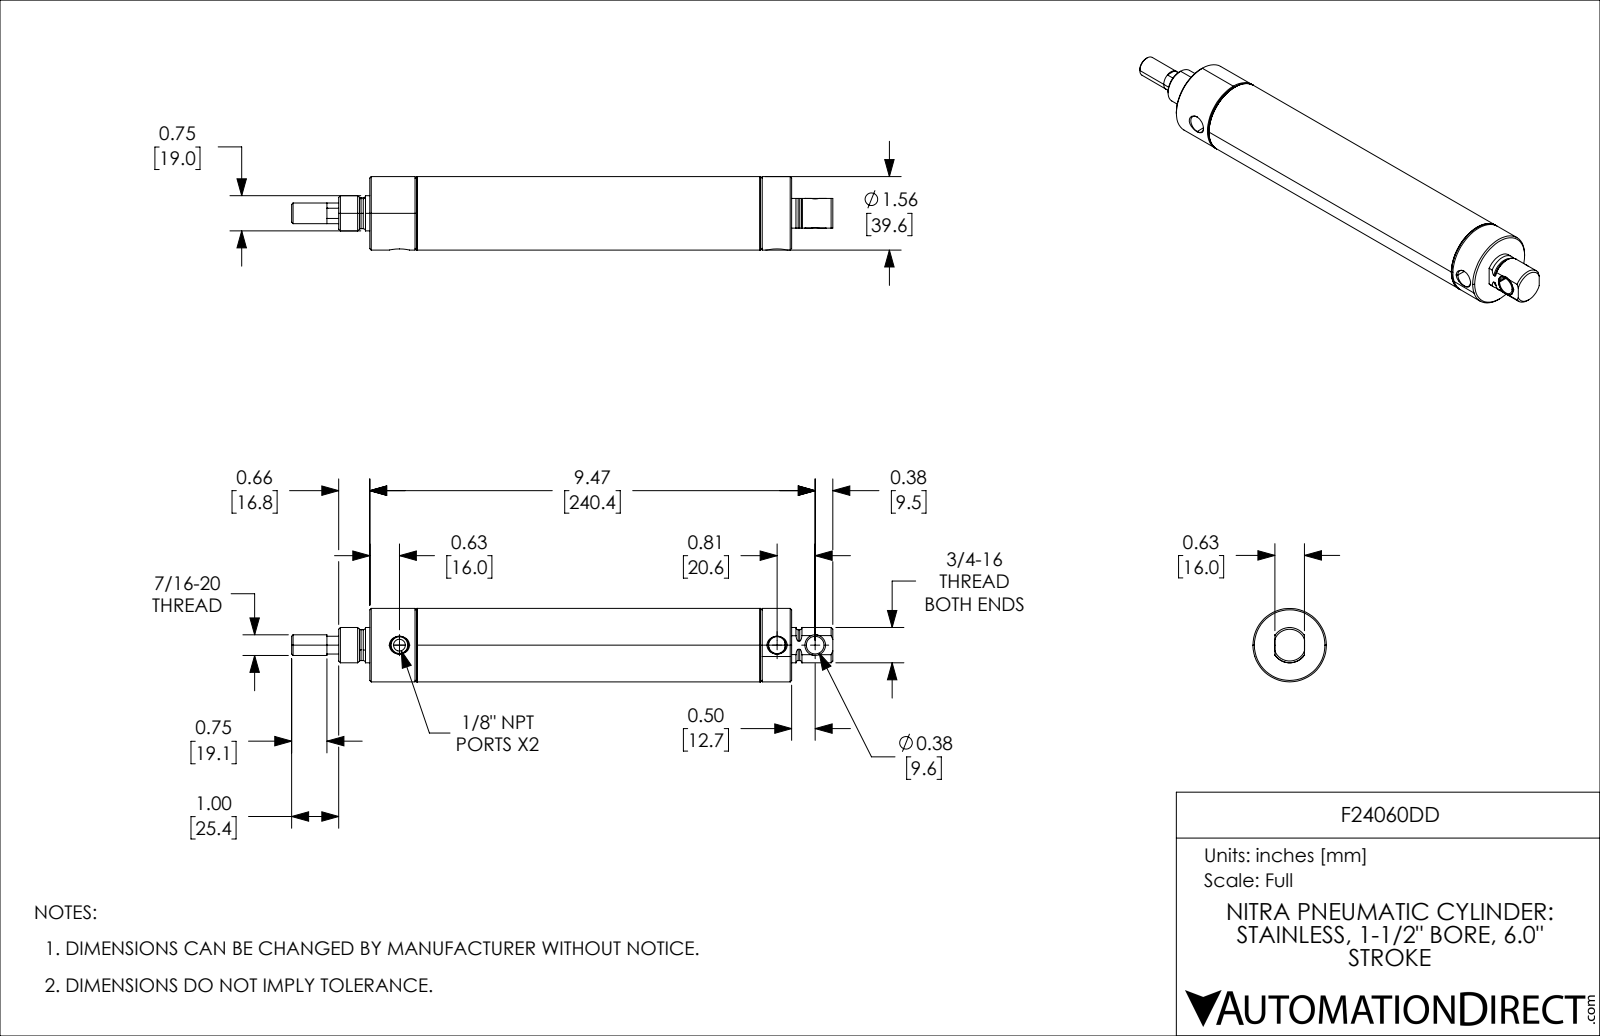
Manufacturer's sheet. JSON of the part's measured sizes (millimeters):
{"part_name": "F24060DD_9; F24060DD_7; F24060DD_5; F24060DD (+2 more)", "step_written_by": "SolidWorks 2021 (CONFIG_CONTROL_DESIGN)", "units": "millimeters", "bodies": {"solids": 5, "faces": 157, "planar": 35, "cylindrical": 58, "other": 64}, "overall_size": [292.1, 39.62, 39.62], "volume_mm3": 121931, "surface_area_mm2": 78291, "round_holes": [[6.35, 1], [9.14, 1], [9.55, 1], [11.15, 1], [11.73, 1], [13.51, 1], [26.97, 1], [36.36, 1]], "round_bosses_or_shafts": [[39.62, 1], [38.39, 1], [19.05, 1], [18.99, 1], [16.61, 1], [16.6, 1], [11.13, 1], [11.11, 1]], "face_to_face_distances": [22.22, 44.45, 152.4, 174.62, 196.85, 22.23, 30.86, 183.26, 205.48, 227.71], "hole_center_spacings": [20.57, 203.84, 224.41]}
